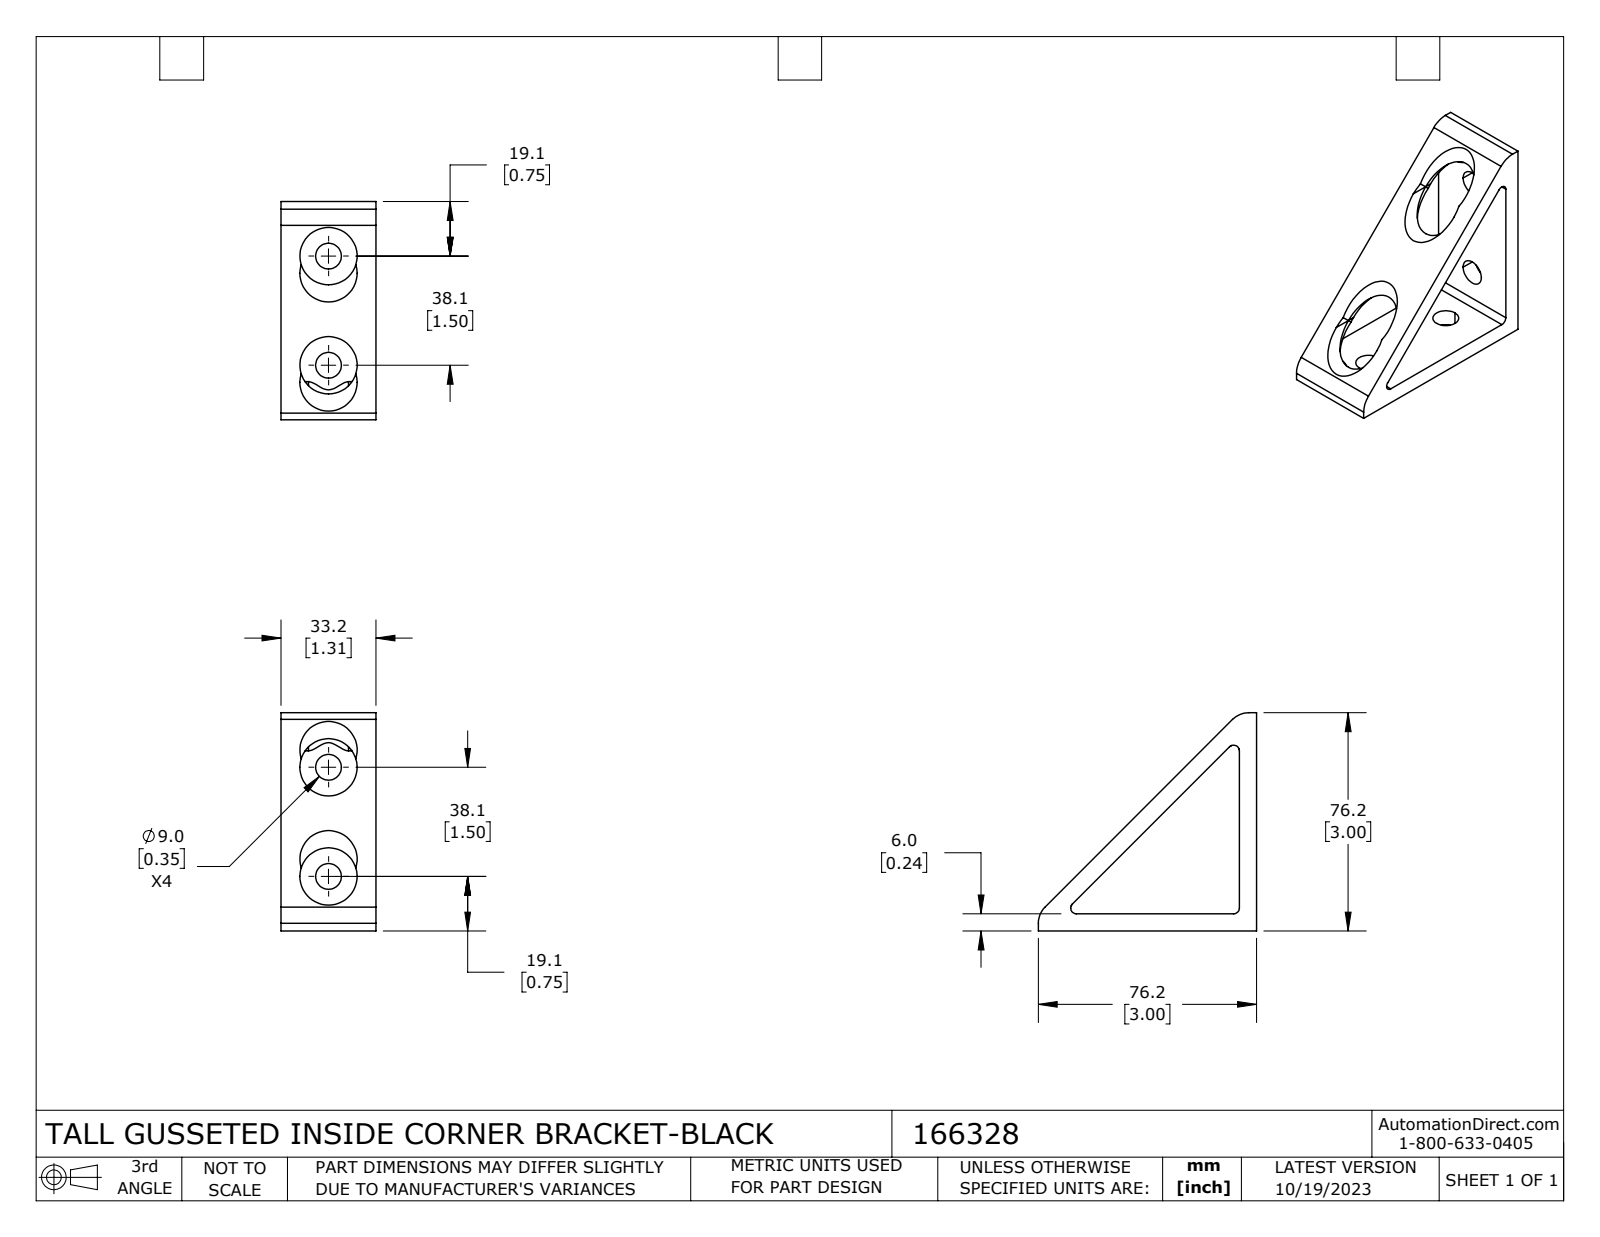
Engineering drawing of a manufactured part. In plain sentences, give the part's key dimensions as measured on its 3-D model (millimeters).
The part is named "166328". Its 3-D file was written by "SolidWorks 2023 (CONFIG_CONTROL_DESIGN)". It is 1 solid with 47 faces: 10 planar, 35 cylindrical and 2 other. Overall it measures 76.2 by 76.2 by 33.2 millimeters. Its volume is 40 201 cubic millimeters and its surface area 17 391 square millimeters. Round holes: 4 of diameter 9, 4 of diameter 20. Partial cylindrical surfaces (rounded edges, fillets, slot ends): 3 of radius 2, 2 of radius 8. The main face-to-face distances are 6, 33.2, 76.2, 70.2. The hole center spacings are 38.1.
